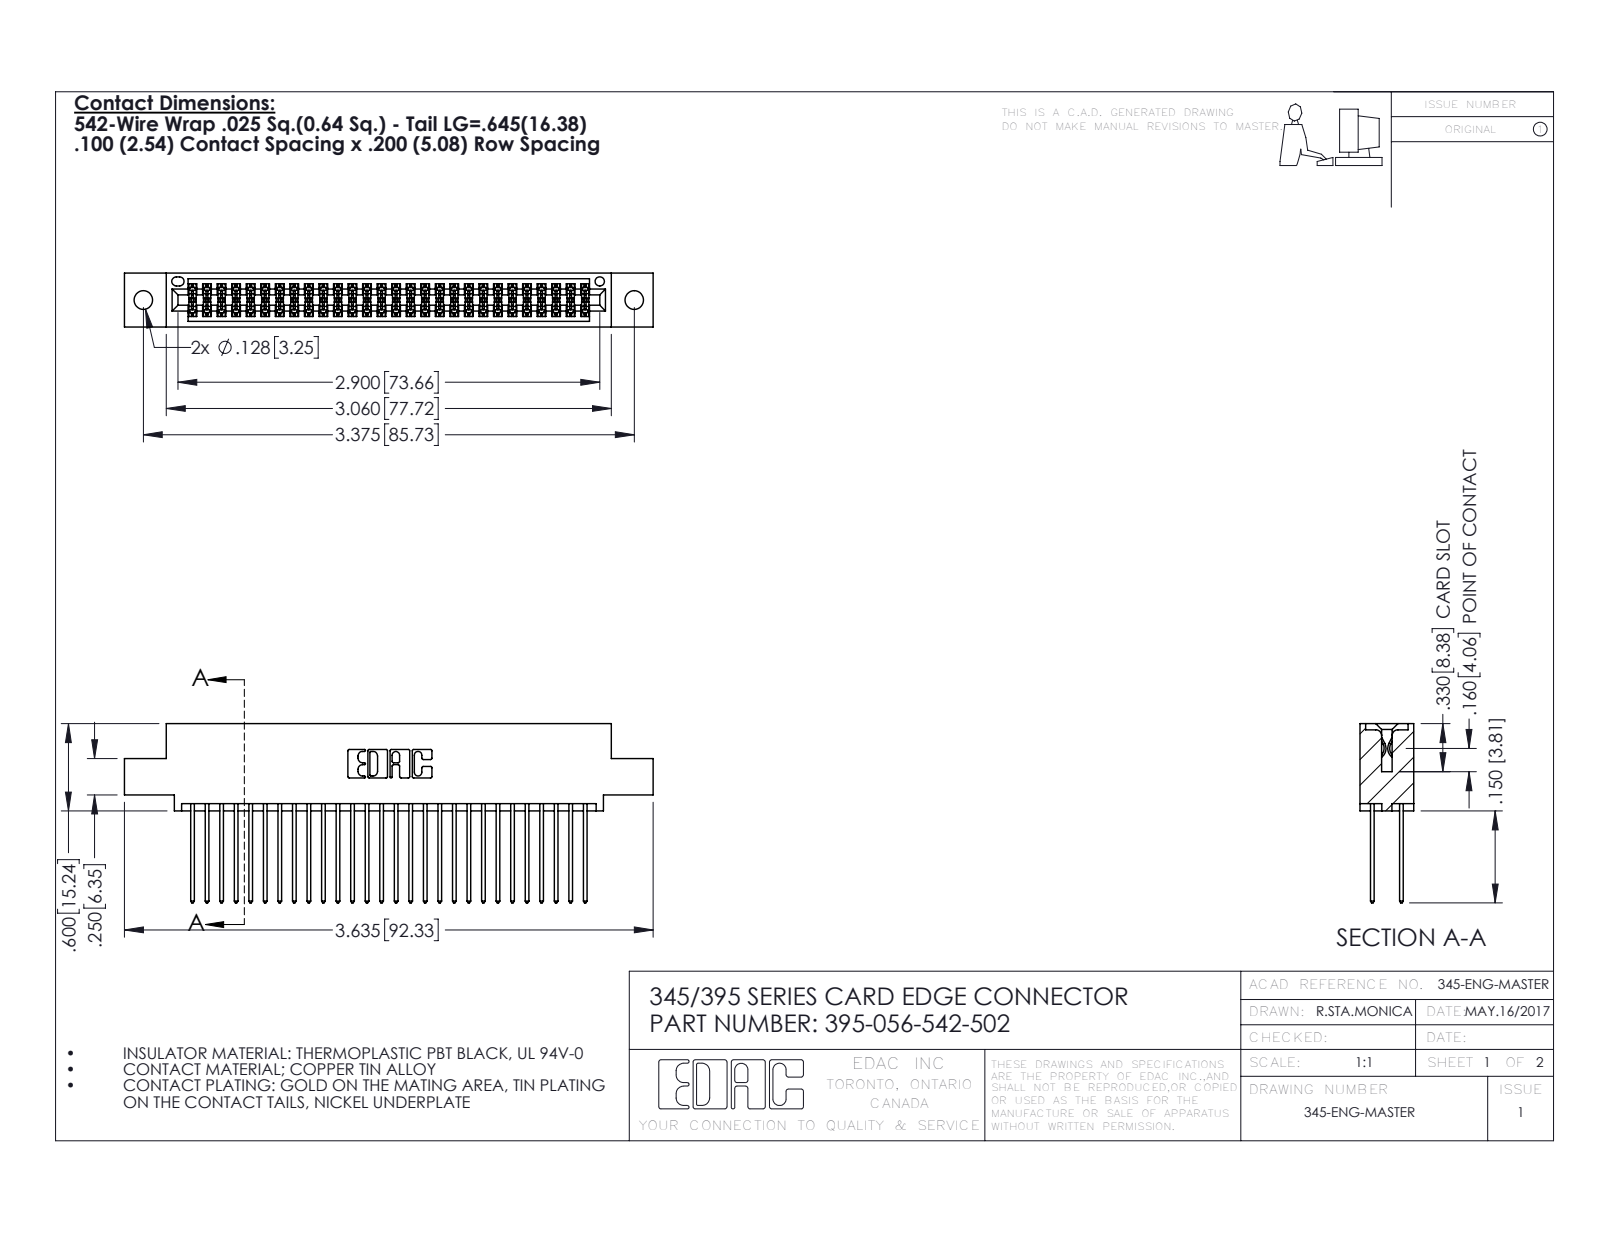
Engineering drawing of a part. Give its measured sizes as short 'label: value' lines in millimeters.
name: 345 Part_0.110 Offset - 0.128 Dia; 395-056-542-502; 345-292-001_345-293-142
written by: SolidWorks 2016 (CONFIG_CONTROL_DESIGN)
unit: mm
bodies: 57 solids, 2930 faces (1932 planar, 998 cylindrical, 0 other)
size: 92.3 × 31.3 × 9.4
volume: 9 000 mm³; area: 14 060 mm²
holes: 2× ⌀3.3, 1× ⌀1.6
rounds: 84× R0.2, 56× R0.3, 22× R0.3, 6× R0.2, 6× R0.8, 3× R0.7, 2× R0.4, 2× R0.5
face distances: 7.6, 1.8, 5.1, 2.5, 6.9, 0.6, 9.4, 5.7, 4.4, 3.8
hole spacings: 6.9, 79.8, 85.7
